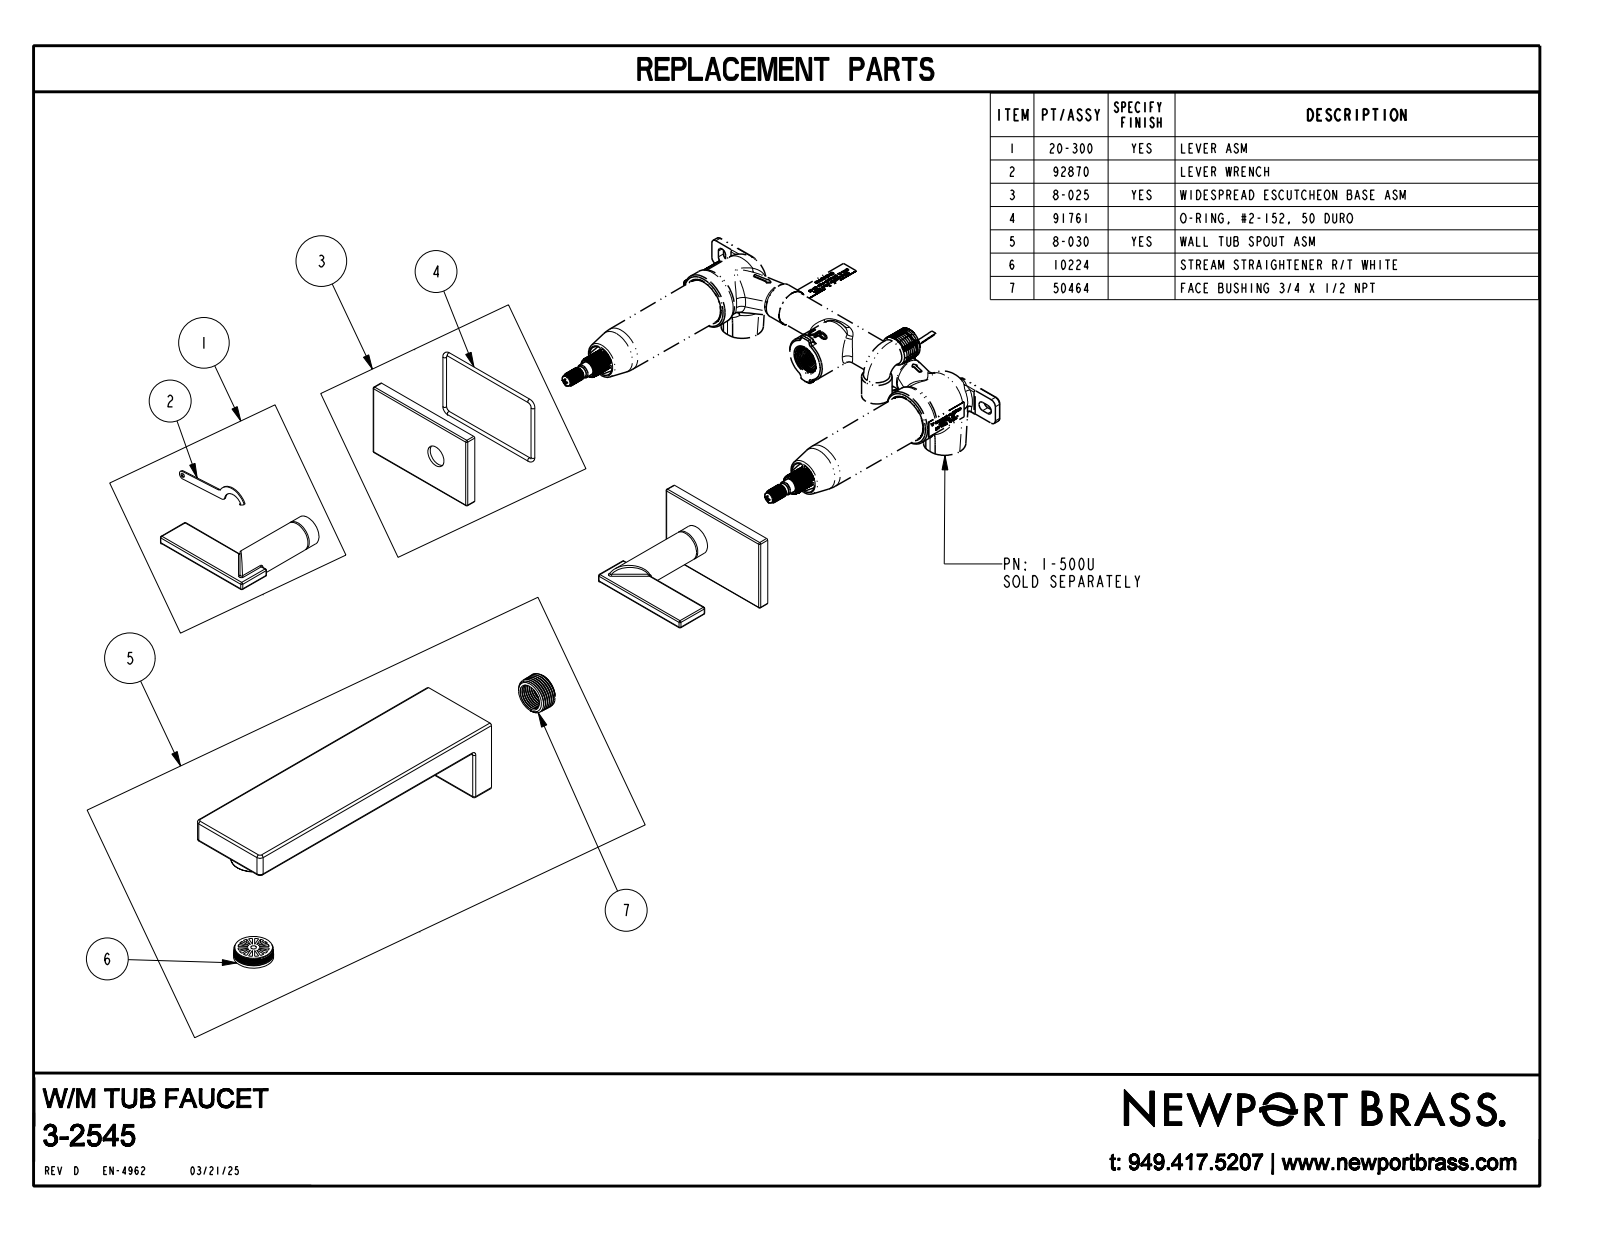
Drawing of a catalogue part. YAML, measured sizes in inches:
part_name: "3-2545_SW0001"
step_written_by: "CREO PARAMETRIC BY PTC INC, 2018400 (AUTOMOTIVE_DESIGN)"
units: inches
bodies: {solids: 3, faces: 191, planar: 45, cylindrical: 84, other: 62}
overall_size: [12.995, 9.438, 8.2]
volume: 28.13
surface_area: 140
round_bosses_or_shafts:
  - {diameter: 0.86, count: 2}
  - {diameter: 0.68, count: 2}
  - {diameter: 1.8, count: 1}
  - {diameter: 1.297, count: 1}
  - {diameter: 1.25, count: 1}
partial_cylinders:
  - {radius: 0.04, count: 42}
  - {radius: 0.06, count: 11}
  - {radius: 0.118, count: 2}
  - {radius: 0.08, count: 1}
face_to_face_distances: [0.67, 0.31, 2.5, 5.452, 4.782, 5.688, 5.018, 0.236, 0.982, 1.218]
